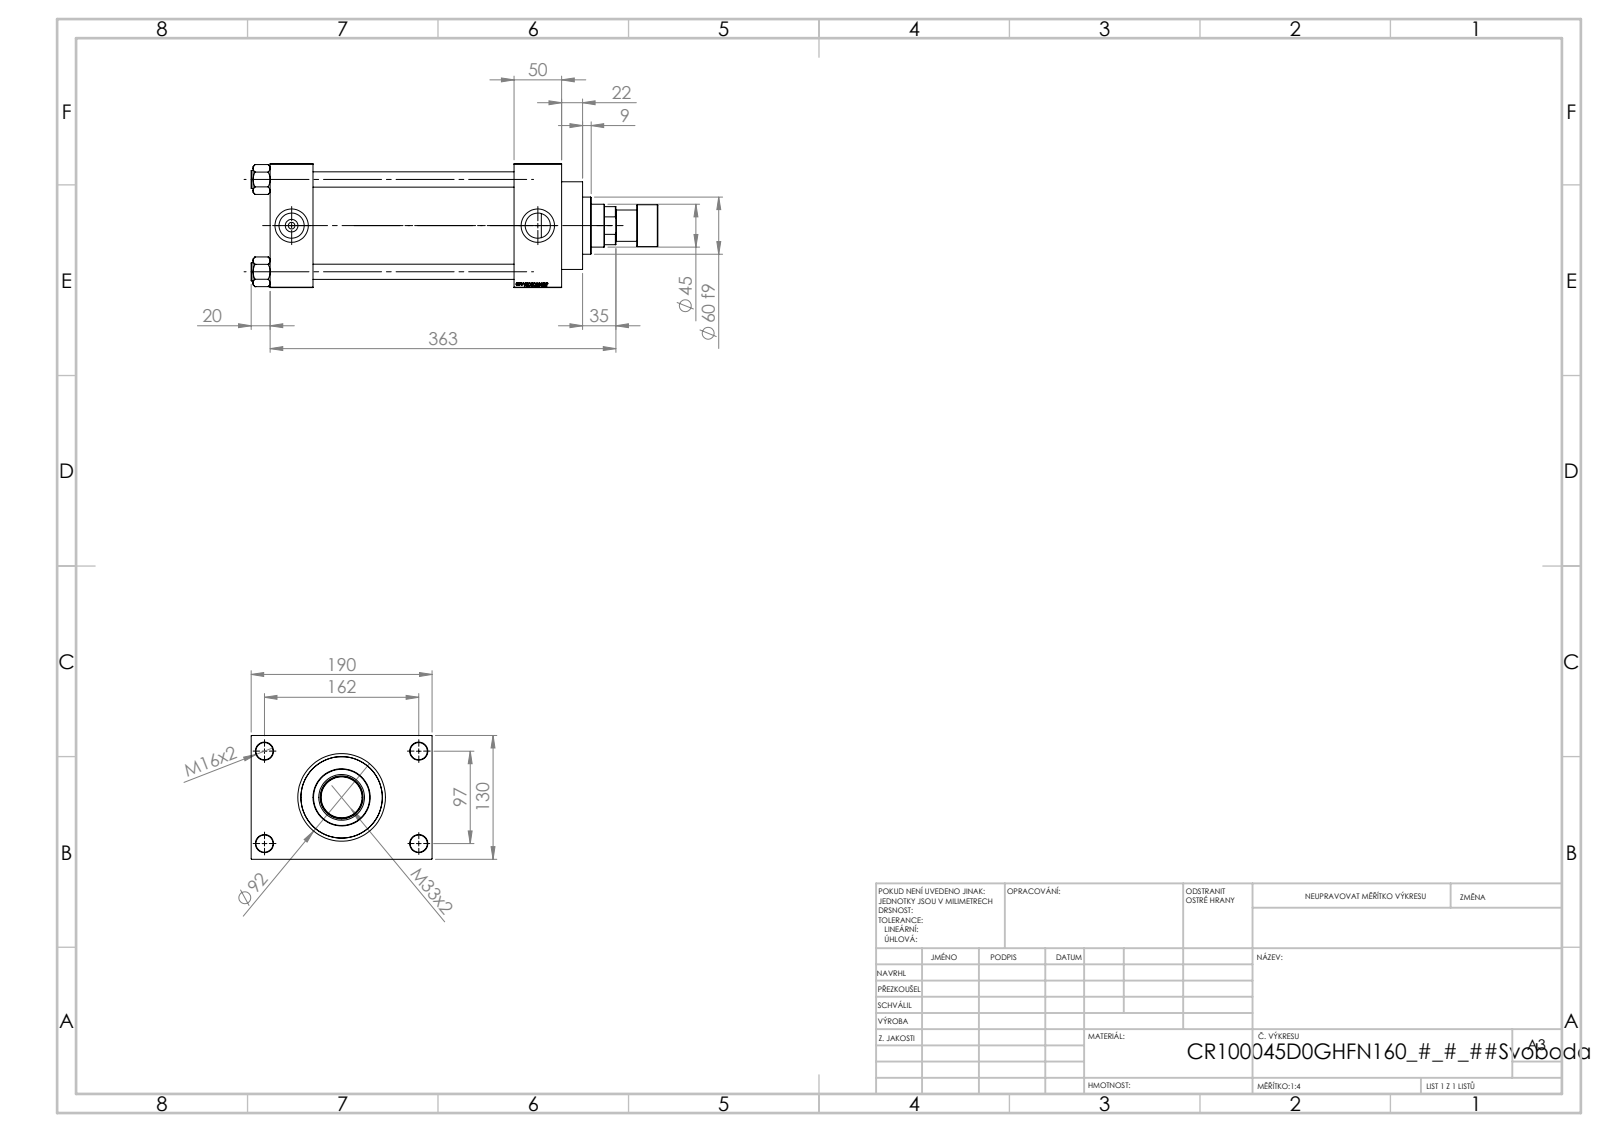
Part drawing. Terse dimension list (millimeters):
name: V215CR_VCP_D; V215CR_D_Body; V215CR_D_TYCINKA; V215CR_ROD_END_F (+2 more)
written by: SolidWorks 2019 (CONFIG_CONTROL_DESIGN)
unit: mm
bodies: 12 solids, 1164 faces (548 planar, 92 cylindrical, 524 other)
size: 427 × 190 × 130
volume: 3 114 000 mm³; area: 501 800 mm²
holes: 4× ⌀16, 4× ⌀18, 2× ⌀7, 2× ⌀26.44, 2× ⌀35, 1× ⌀31.5, 1× ⌀45, 1× ⌀48, 1× ⌀76, 1× ⌀85.5, 1× ⌀100
bosses: 4× ⌀19, 1× ⌀106, 1× ⌀92, 1× ⌀60, 1× ⌀44, 1× ⌀33
face distances: 130, 45, 256, 211, 306, 261, 50, 160, 30, 96
hole spacings: 32.55, 68.52, 94.41, 96.9, 102.27, 129.45, 161.73, 97
